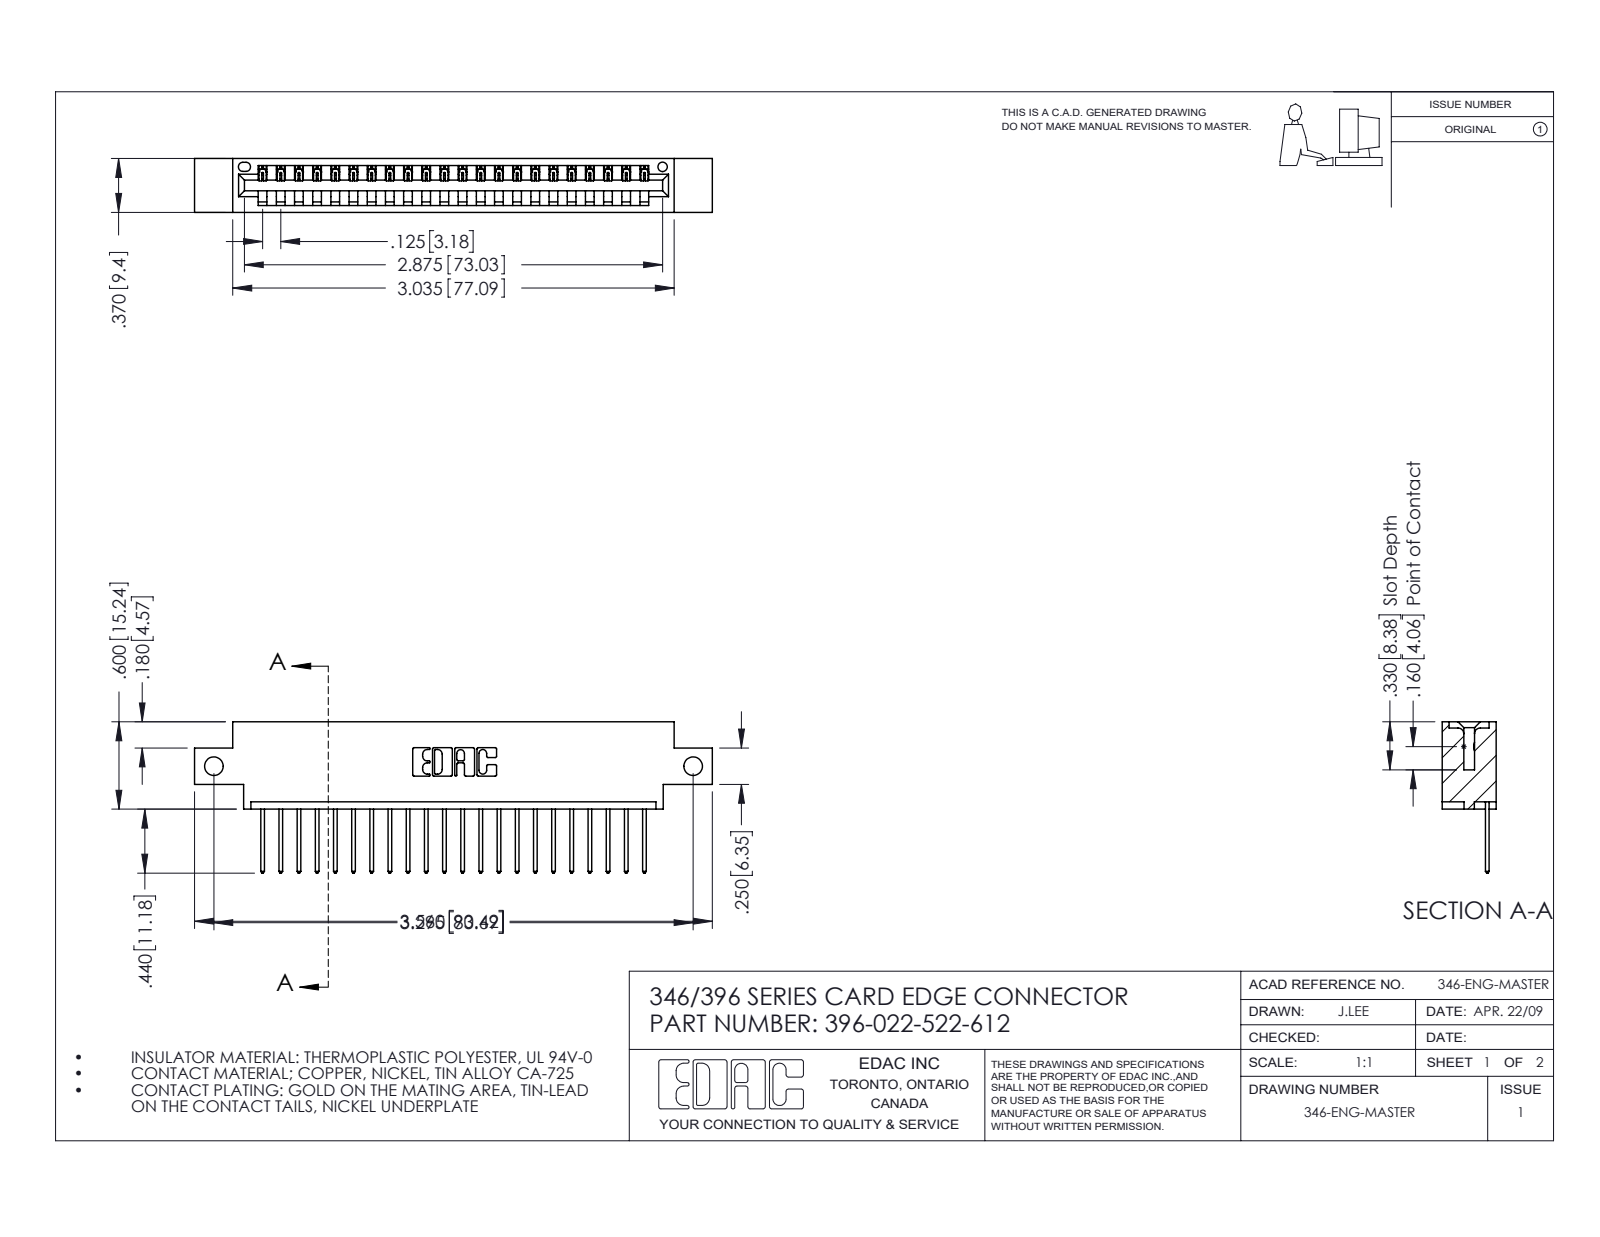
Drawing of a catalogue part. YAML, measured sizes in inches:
part_name: "346 Part_0.170 Offset - Side Mount; 396-022-522-612; 345-292-001_345-293-122"
step_written_by: "SolidWorks 2016 (CONFIG_CONTROL_DESIGN)"
units: inches
bodies: {solids: 23, faces: 1402, planar: 960, cylindrical: 442, other: 0}
overall_size: [3.56, 1.04, 0.37]
volume: 0.505
surface_area: 15.85
round_holes:
  - {diameter: 0.128, count: 2}
  - {diameter: 0.064, count: 1}
partial_cylinders:
  - {radius: 0.006, count: 44}
  - {radius: 0.01, count: 44}
  - {radius: 0.01, count: 22}
  - {radius: 0.007, count: 6}
  - {radius: 0.031, count: 6}
  - {radius: 0.026, count: 3}
  - {radius: 0.031, count: 2}
  - {radius: 0.04, count: 2}
face_to_face_distances: [0.048, 0.322, 0.37, 0.25, 0.072, 0.298, 0.025, 0.148, 0.222, 0.1]
hole_center_spacings: [3.295]
